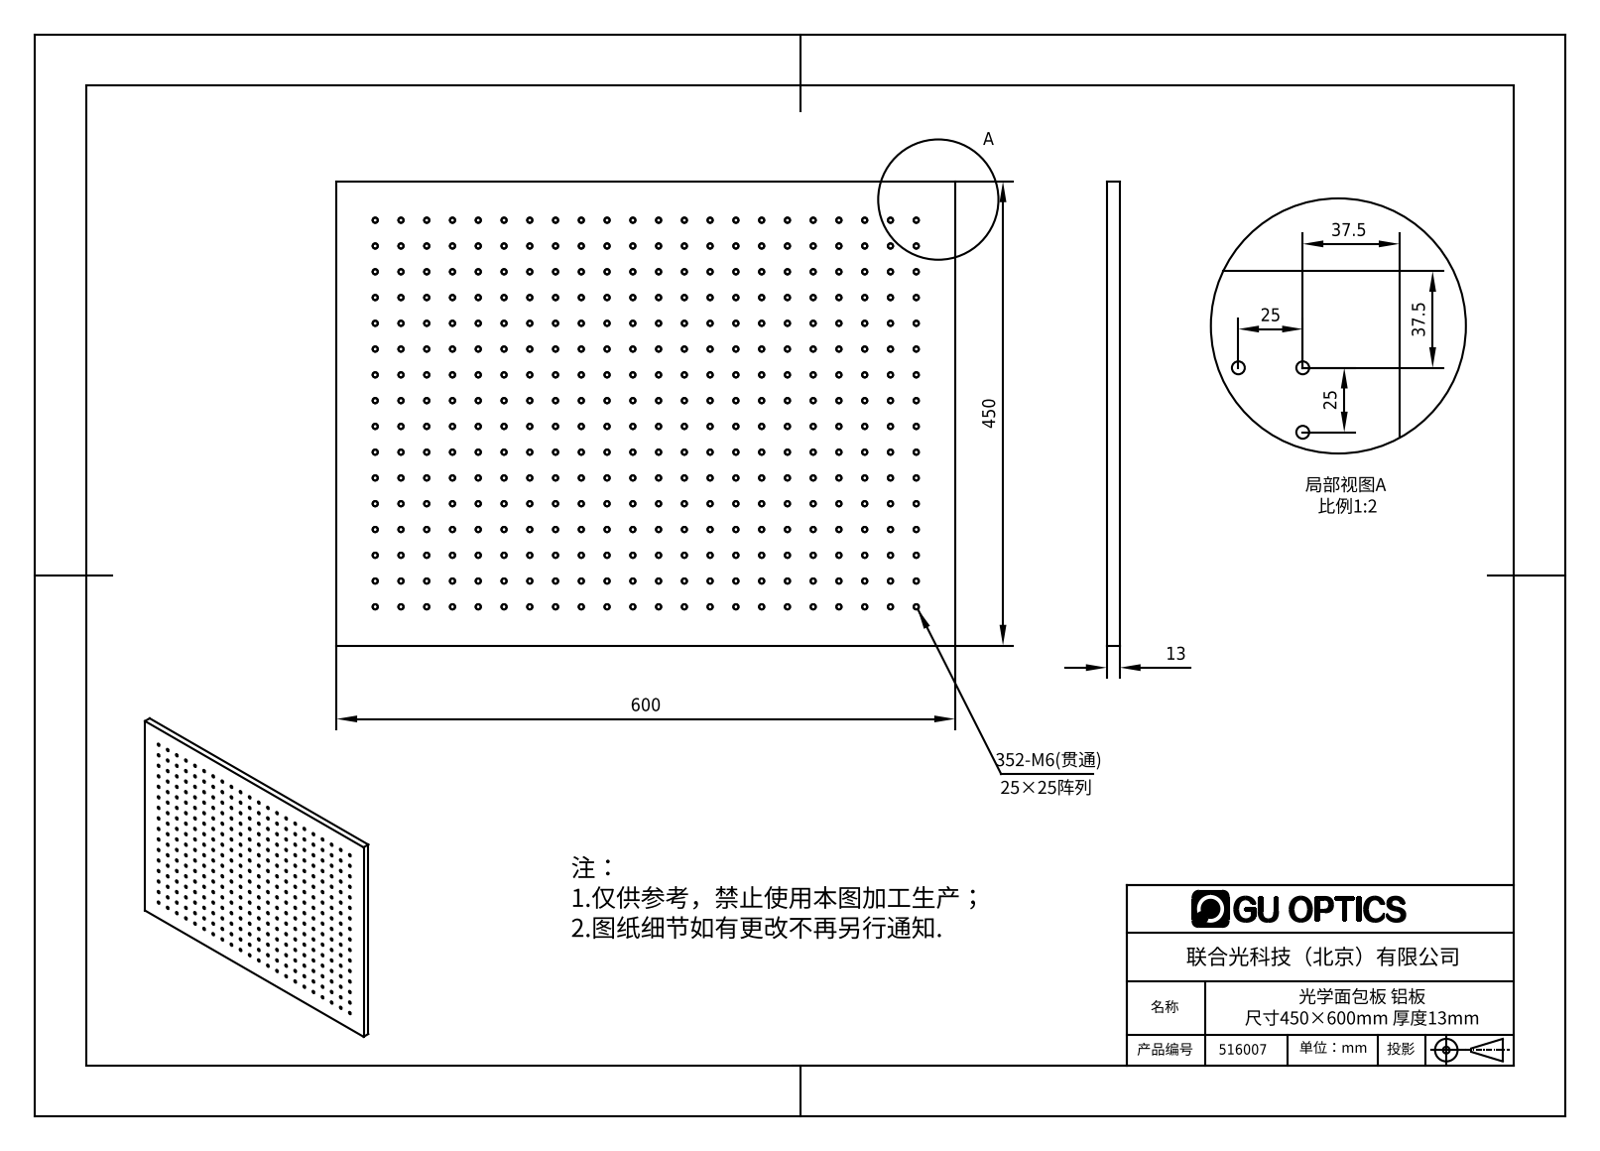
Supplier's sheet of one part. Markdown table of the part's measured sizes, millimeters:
| quantity | value |
| --- | --- |
| part name | 516007 |
| STEP written by | SolidWorks 2020 (CONFIG_CONTROL_DESIGN) |
| units | millimeters |
| bodies | 1 solid, 421 faces (14 planar, 407 cylindrical, 0 other) |
| overall size | 600 × 450 × 13 |
| volume | 3 404 000 mm³ |
| surface area | 634 111 mm² |
| round holes (diameter × count) | 5 × 391, 5.8 × 8, 11 × 8 |
| main face-to-face distances | 13, 450, 600, 6.5 |
| hole center spacings | 50, 100, 55.9, 150, 103.08, 200, 152.07, 250 |
